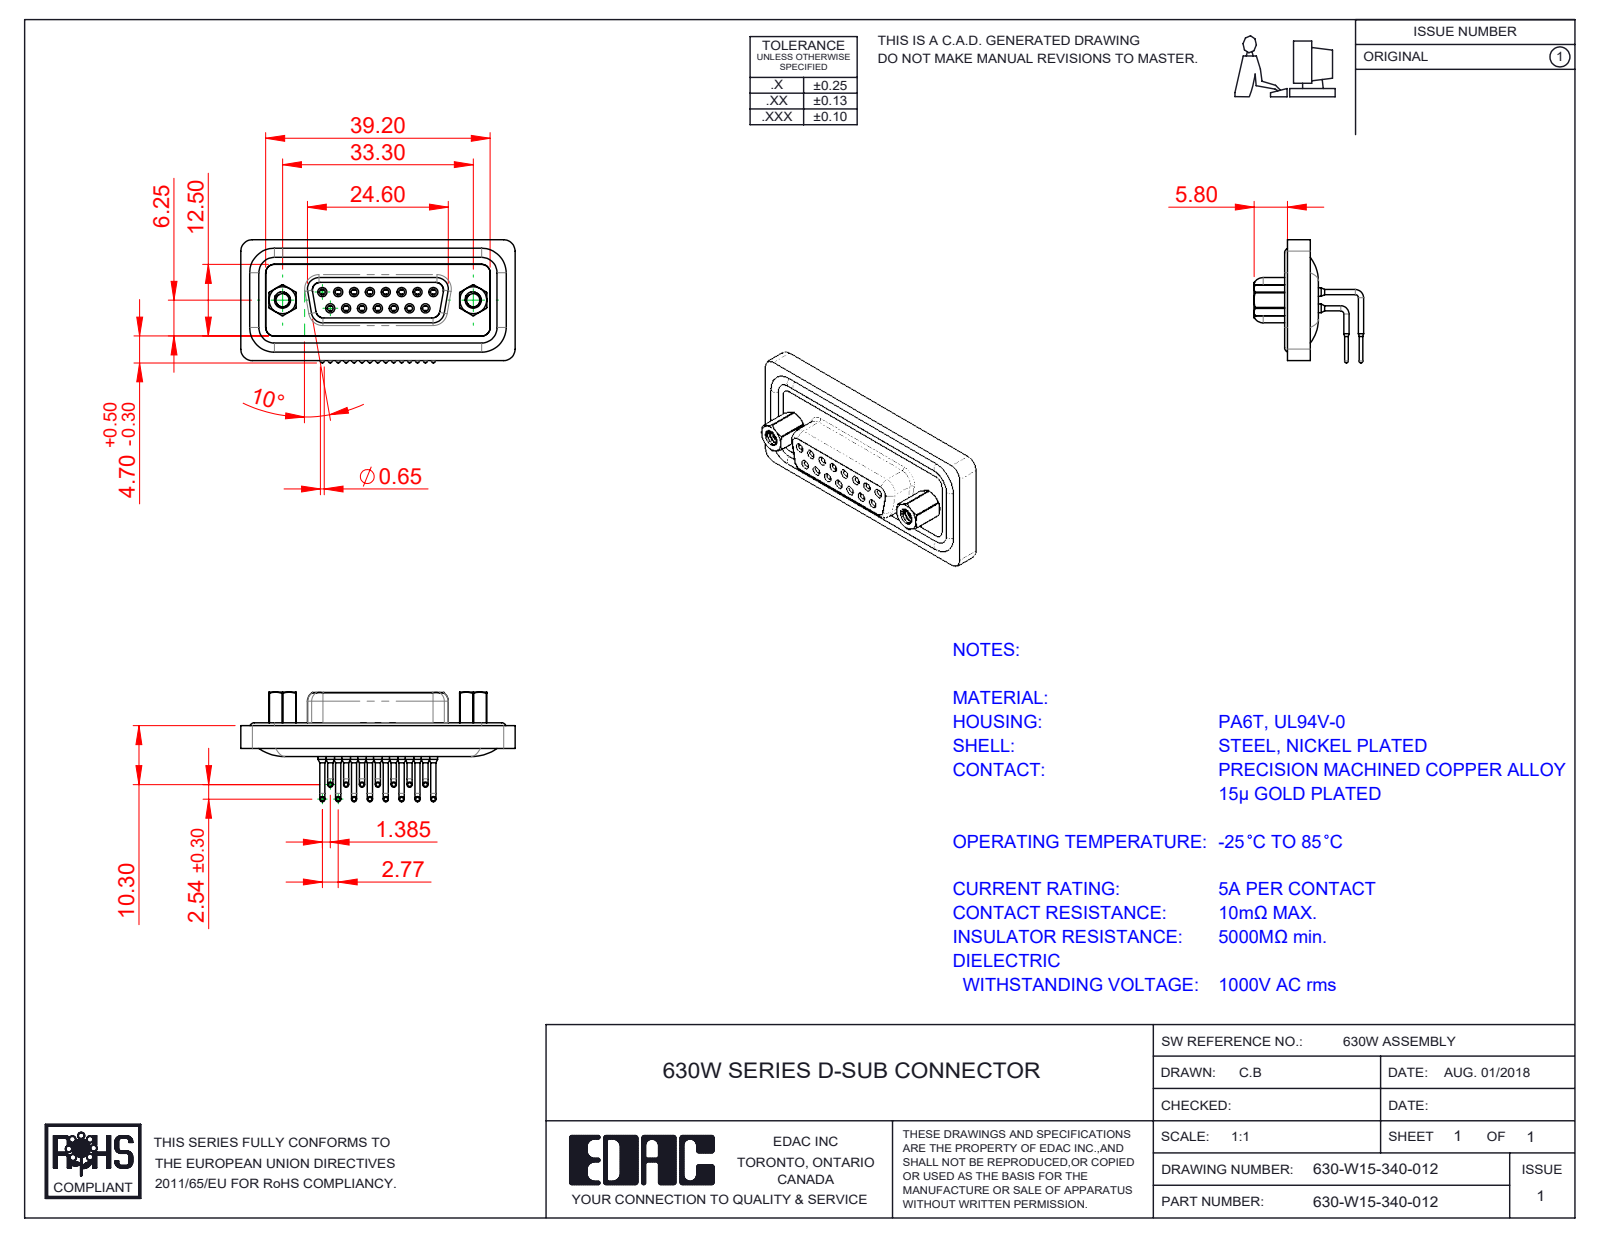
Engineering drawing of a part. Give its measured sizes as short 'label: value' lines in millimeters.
name: 630W Waterproof Housing_15 Contacts; 630W Contact Row 2; 630W 4-40 Threaded Rivet_Stabilizer; 630W 4-40 Hex Standoff (+4 more)
written by: SolidWorks 2016 (CONFIG_CONTROL_DESIGN)
unit: mm
bodies: 23 solids, 1240 faces (326 planar, 587 cylindrical, 327 other)
size: 47.89 × 21.5 × 19.14
volume: 5 562 mm³; area: 9 705 mm²
holes: 15× ⌀1, 15× ⌀1.1, 15× ⌀1.5, 15× ⌀1.7, 15× ⌀1.8, 15× ⌀2, 2× ⌀2.26, 2× ⌀2.29, 2× ⌀4, 2× ⌀4.8, 2× ⌀5
bosses: 30× ⌀0.9, 19× ⌀1.6, 15× ⌀1.5, 15× ⌀0.65, 2× ⌀4.9, 2× ⌀2.79, 1× ⌀5
rounds: 16× R2, 14× R1.5, 8× R1.35, 6× R2.7, 4× R0.5, 4× R0.9, 4× R1.6, 4× R1.75
face distances: 0.4, 1.8, 1.6, 1.1, 2.5, 2.9, 0.5, 7.45, 13.65, 9.8
hole spacings: 3.16, 2.77, 5.54, 8.31, 3.17, 3.15, 11.08, 5.03
